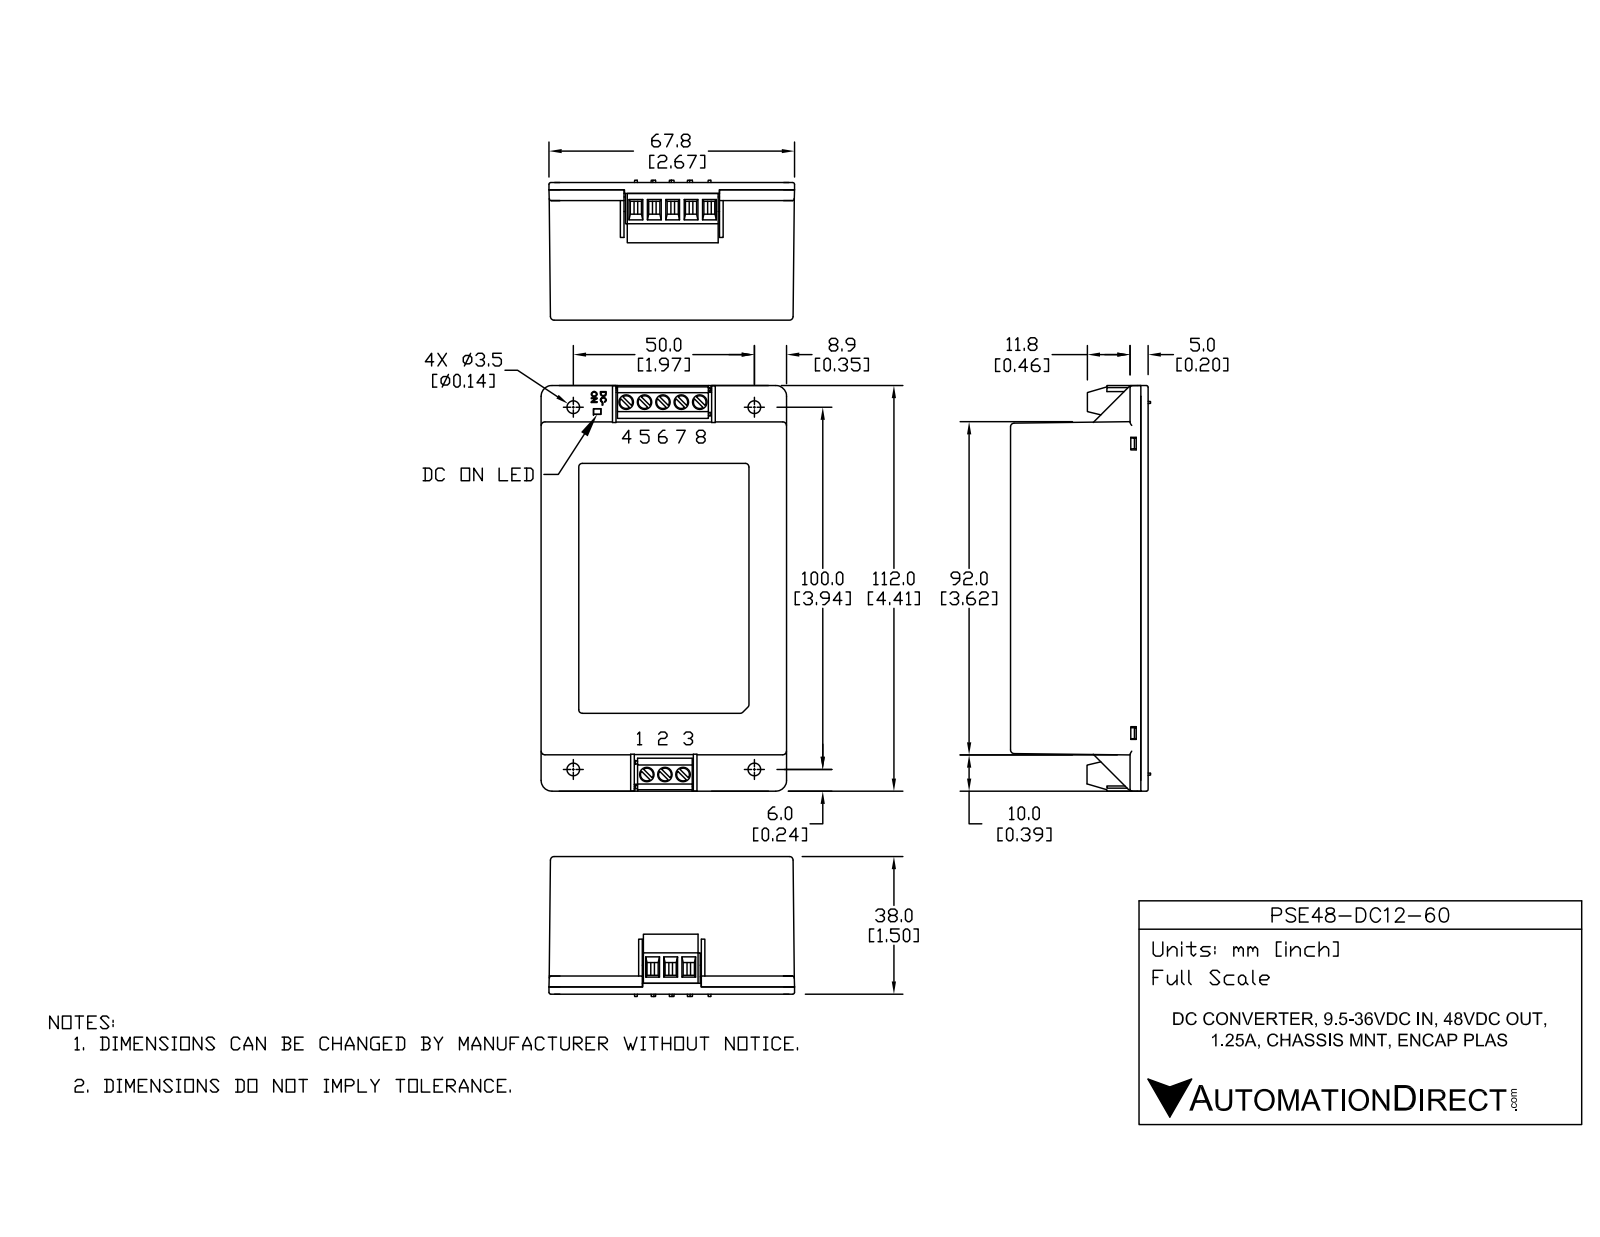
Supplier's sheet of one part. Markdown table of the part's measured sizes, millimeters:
| quantity | value |
| --- | --- |
| part name | PSE48-DC12-60 |
| STEP written by | SolidWorks 2015 (AUTOMOTIVE_DESIGN) |
| units | millimeters |
| bodies | 0 solids, 390 faces (282 planar, 89 cylindrical, 19 other) |
| overall size | 112.92 × 69.3 × 37.06 |
| round holes (diameter × count) | 4 × 10, 3.5 × 4, 2.46 × 1, 4.08 × 1, 6.5 × 1 |
| round bosses / shafts (diameter × count) | 1.5 × 4, 5 × 1 |
| partial cylindrical surfaces (radius × count) | 1 × 17, 0.5 × 8, 2.15 × 4, 2.65 × 4, 3 × 4, 3.25 × 3 |
| main face-to-face distances | 1, 0.98, 35, 34, 0.7, 1.02, 1.7, 33.3, 34.99, 33.99 |
| hole center spacings | 5.08, 10.16, 50, 102.13, 102.29, 5, 15.24, 100 |
